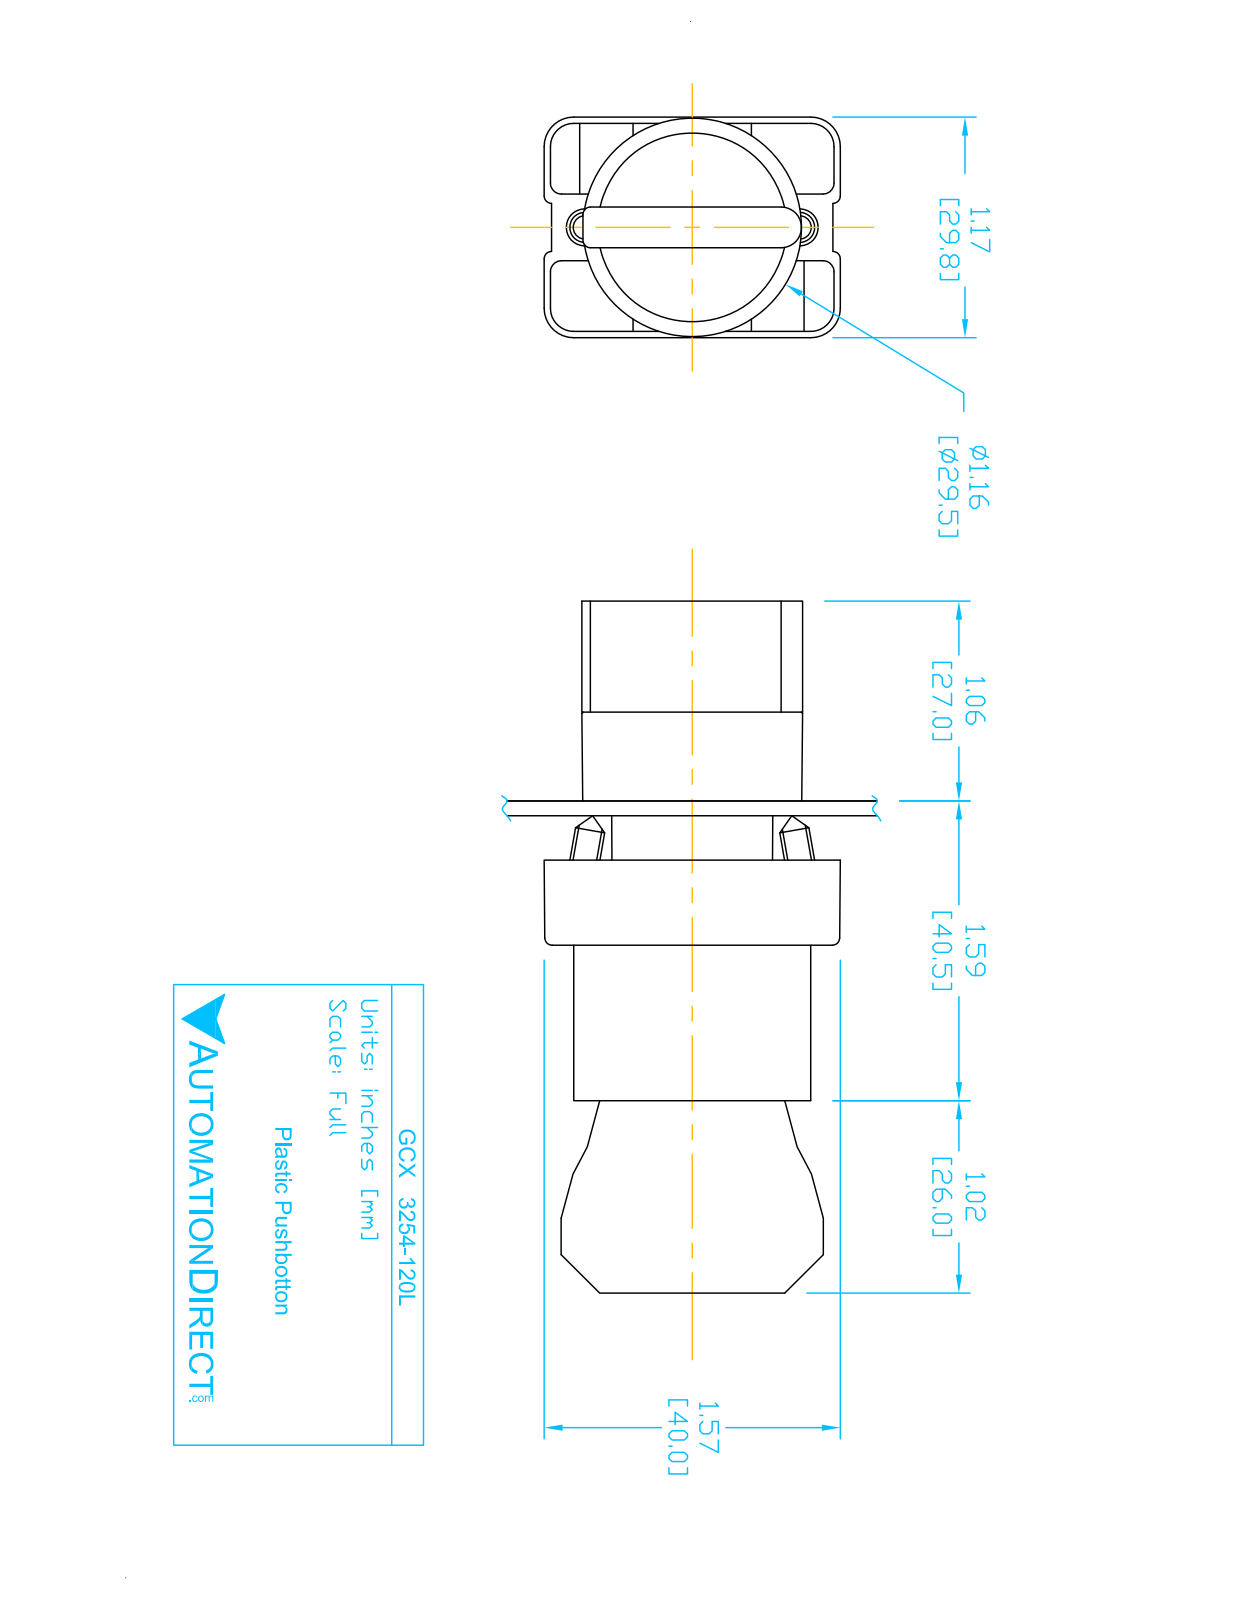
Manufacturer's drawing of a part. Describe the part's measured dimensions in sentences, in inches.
The part is named "GCX3254-120L; ecx1040; ECX1050; ECX3029-2 (+1 more)". Its 3-D file was written by "SolidWorks 2016 (AUTOMOTIVE_DESIGN)". It is 8 solids with 445 faces: 263 planar, 151 cylindrical and 31 other. Overall it measures 3.653 by 1.581 by 1.177 inches. Its volume is 2.799 cubic inches and its surface area 39 square inches. Round holes: 2 of diameter 0.079, 2 of diameter 0.124, 2 of diameter 0.13, 1 of diameter 0.087, 1 of diameter 0.197, 1 of diameter 0.469, 1 of diameter 0.878, 1 of diameter 0.888, 1 of diameter 1.024. Round bosses or shafts: 4 of diameter 0.157, 1 of diameter 1.175, 1 of diameter 1.004, 1 of diameter 0.945, 1 of diameter 0.856, 1 of diameter 0.78, 1 of diameter 0.504. Partial cylindrical surfaces (rounded edges, fillets, slot ends): 24 of radius 0.059, 12 of radius 0.041, 12 of radius 0.124, 12 of radius 0.157, 9 of radius 0.039, 2 of radius 0.128, 1 of radius 0.02, 1 of radius 0.063. The main face-to-face distances are 0.827, 2.02, 1.193, 0.579, 1.244, 1.171, 0.472, 0.469, 0.031, 0.033. The hole center spacings are 0.236, 0.544, 0.472, 0.49.
